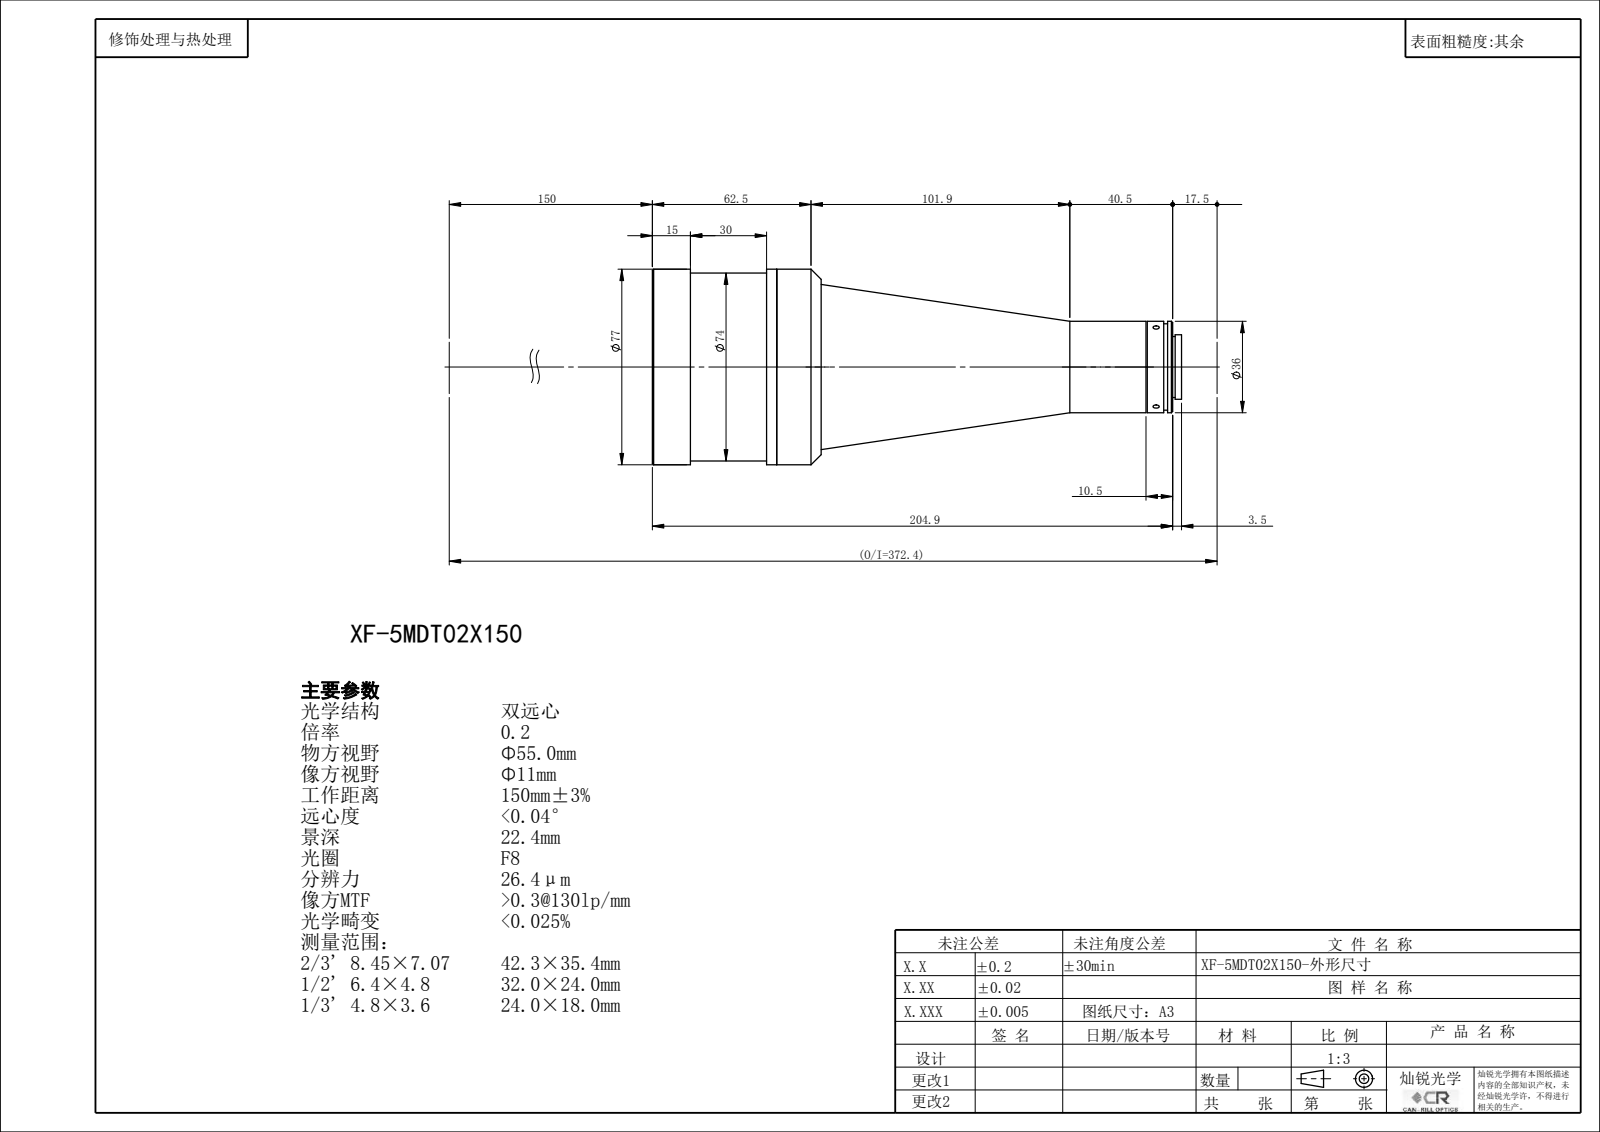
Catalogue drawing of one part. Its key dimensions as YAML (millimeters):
part_name: "XF-5MDT02X150"
step_written_by: "SolidWorks 2014 (CONFIG_CONTROL_DESIGN)"
units: millimeters
bodies: {solids: 0, faces: 96, planar: 38, cylindrical: 42, other: 16}
overall_size: [208.44, 77, 77]
round_holes:
  - {diameter: 2.5, count: 3}
  - {diameter: 16, count: 1}
  - {diameter: 19.4, count: 1}
  - {diameter: 21.4, count: 1}
  - {diameter: 63, count: 1}
  - {diameter: 65, count: 1}
  - {diameter: 70, count: 1}
round_bosses_or_shafts:
  - {diameter: 77, count: 1}
  - {diameter: 74, count: 1}
  - {diameter: 36, count: 1}
  - {diameter: 34, count: 1}
  - {diameter: 28, count: 1}
  - {diameter: 25.4, count: 1}
  - {diameter: 24, count: 1}
face_to_face_distances: [49, 2, 202.94, 153.94, 204.94, 155.94, 3.33, 45.67, 199.61, 201.61]
